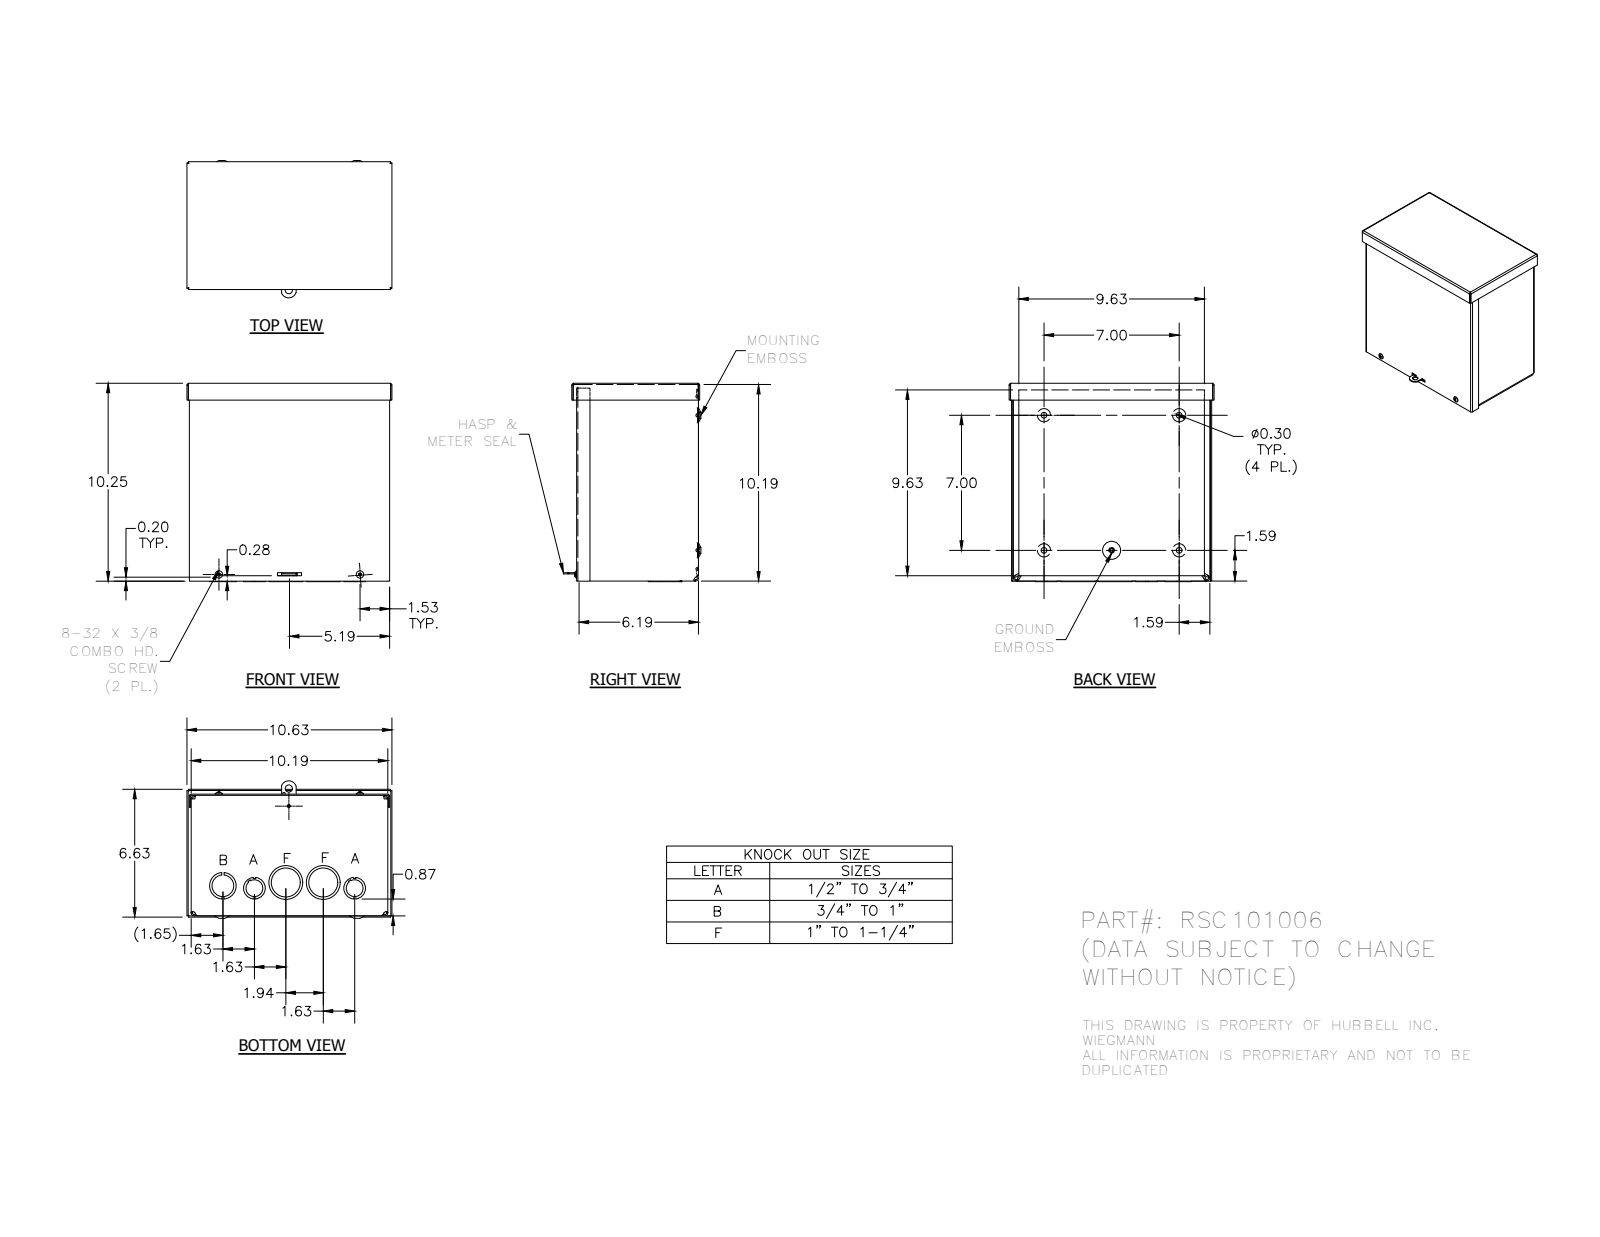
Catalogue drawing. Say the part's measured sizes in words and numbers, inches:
The part is named "RSC101006; RSC101006_WRAP; RSC1010_LID; RSC1006_CAP (+4 more)". Its 3-D file was written by "Autodesk Inventor 2012 (AUTOMOTIVE_DESIGN)". It is 7 solids with 518 faces: 245 planar, 129 cylindrical and 144 other. Overall it measures 10.625 by 10.281 by 7.125 inches. Its volume is 37.95 cubic inches and its surface area 1 241 square inches. Round holes: 4 of diameter 0.3, 4 of diameter 0.313, 3 of diameter 1.125, 2 of diameter 0.125, 2 of diameter 0.148, 2 of diameter 0.875, 2 of diameter 1.5, 2 of diameter 1.75, 1 of diameter 0.156, 1 of diameter 0.165, 1 of diameter 0.375, 1 of diameter 1.375. Round bosses or shafts: 2 of diameter 0.384, 2 of diameter 0.164, 1 of diameter 0.229. Partial cylindrical surfaces (rounded edges, fillets, slot ends): 10 of radius 0.01, 8 of radius 0.031, 8 of radius 0.093, 8 of radius 0.125, 8 of radius 0.187, 4 of radius 0.031, 4 of radius 0.055, 4 of radius 0.062. The main face-to-face distances are 0.062, 10.126, 0.062, 6.249, 10.188, 6.187, 0.063, 0.124, 6.312, 6.25. The hole center spacings are 7, 1.072, 1.261, 1.656, 3.5, 3.582, 7.313, 7.826.
